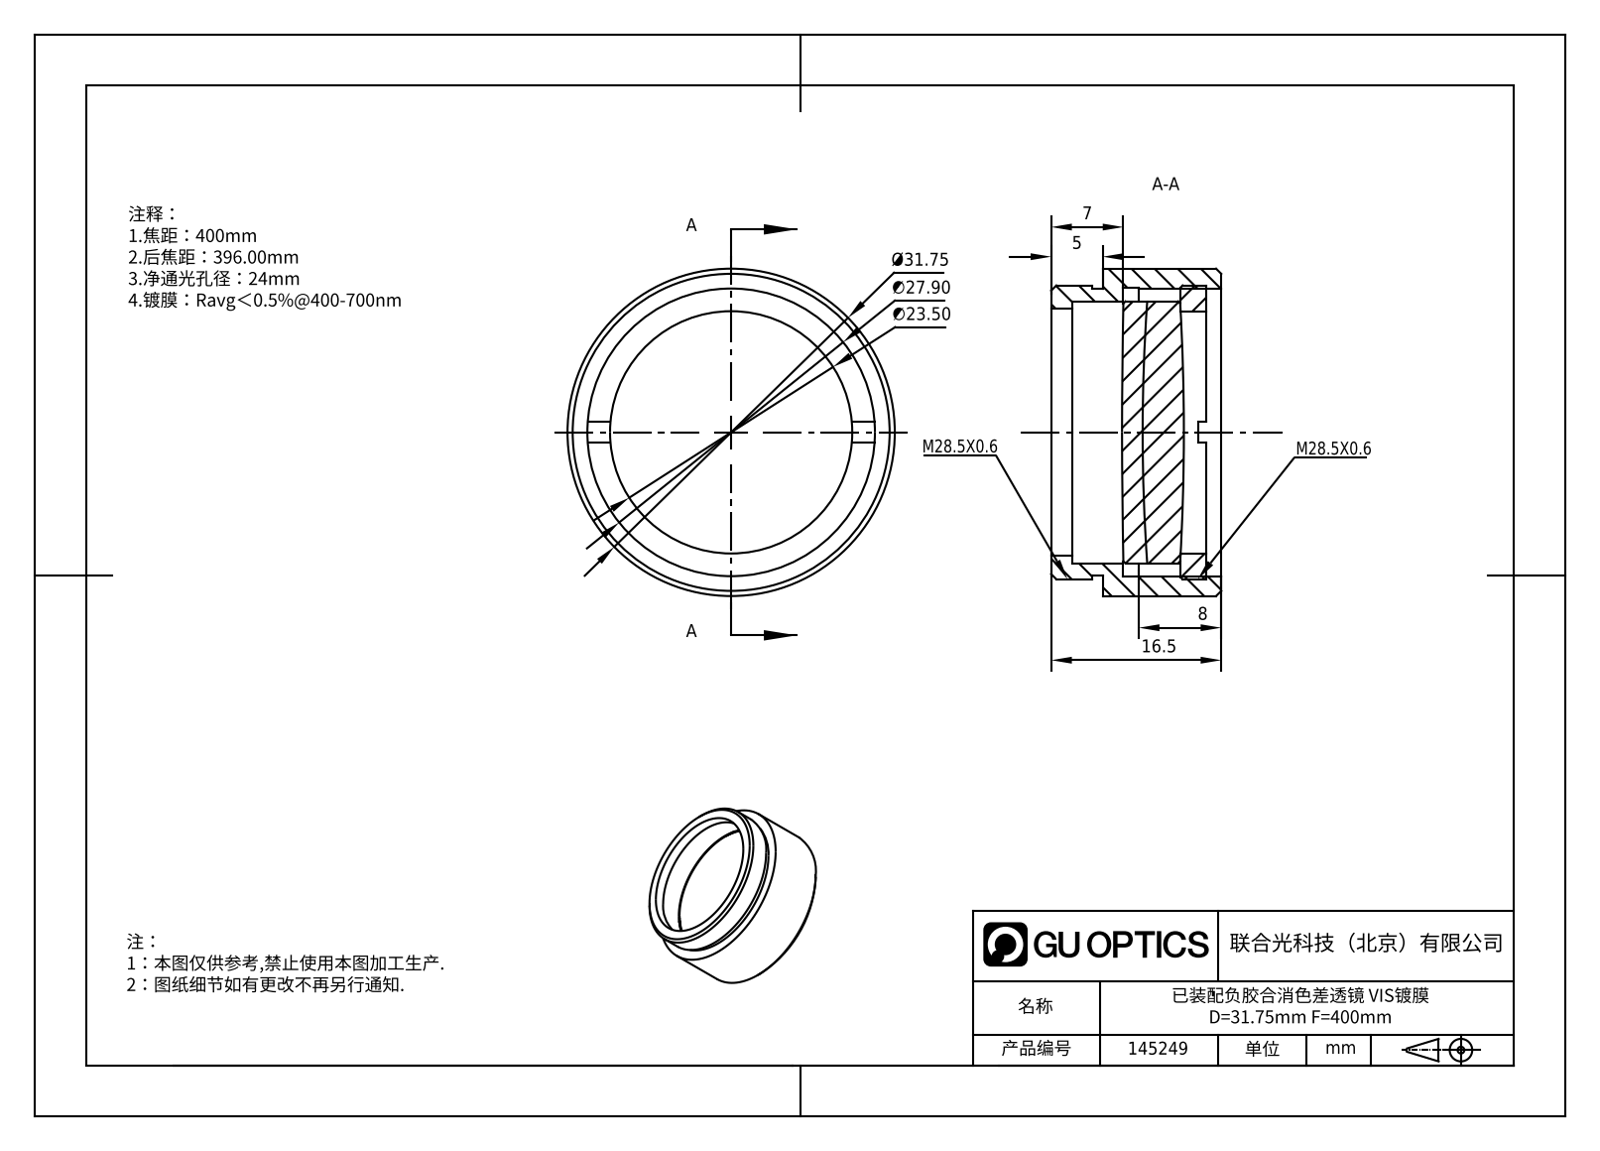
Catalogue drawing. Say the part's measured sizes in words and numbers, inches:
The part is named "M28.5x0.6ѹȦ; APD-ML25-400-VIS; M28.5x0.6安装环PN35020-LM254-D1; GL31-025B-400-VIS_Solidworks". Its 3-D file was written by "SolidWorks 2022 (AUTOMOTIVE_DESIGN)". It is 4 solids with 56 faces: 16 planar, 22 cylindrical and 18 other. Overall it measures 1.25 by 1.25 by 0.65 inches. Its volume is 0.391 cubic inches and its surface area 10.74 square inches. Round holes: 1 of diameter 0.925, 1 of diameter 0.945, 1 of diameter 1.098, 1 of diameter 1.102. Round bosses or shafts: 1 of diameter 1.25, 1 of diameter 1.122, 1 of diameter 1.094, 1 of diameter 1. The main face-to-face distances are 0.079, 0.197, 0.098, 0.297, 0.396, 0.494, 0.593, 0.65, 0.453, 0.156.
